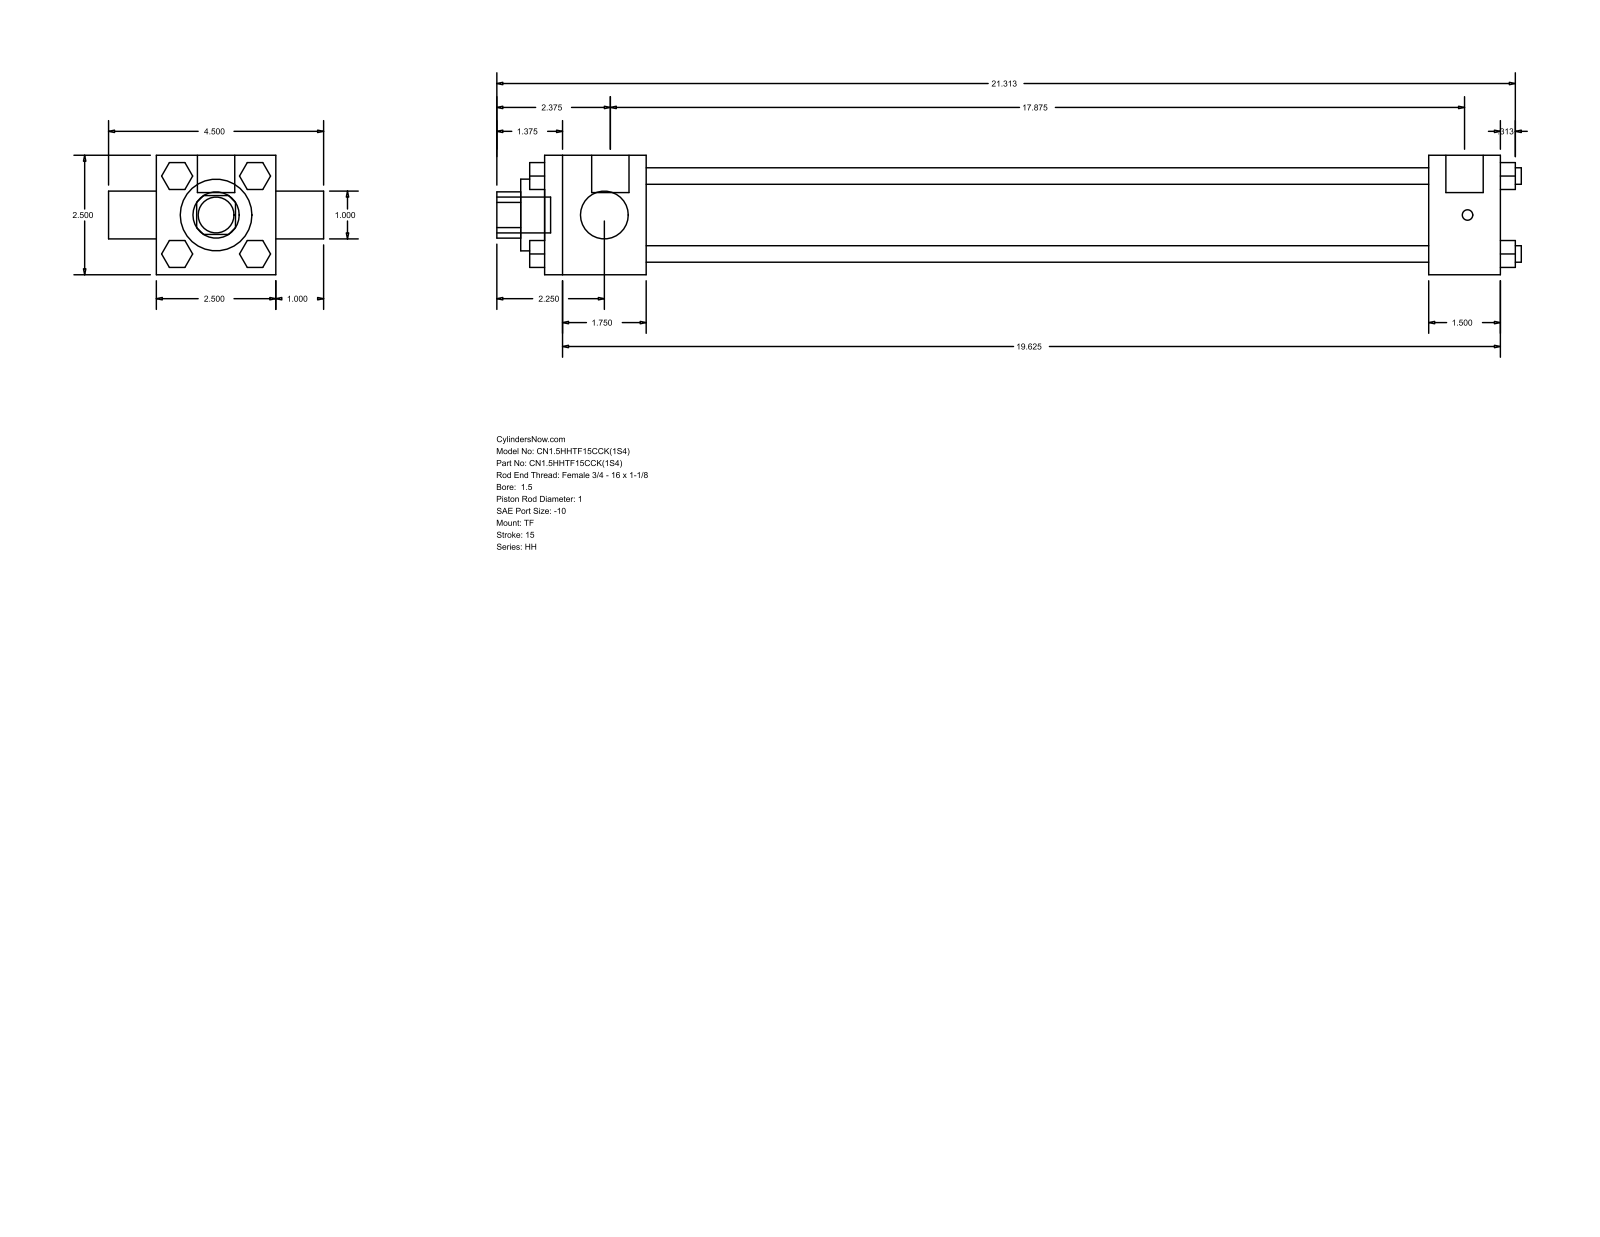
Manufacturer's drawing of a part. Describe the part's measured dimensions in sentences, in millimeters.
The part is named "HH_TF__0150_1". Its 3-D file was written by "GSSL Pune (CONFIG_CONTROL_DESIGN)". It is 0 solids with 120 faces: 92 planar, 28 cylindrical and 0 other. Overall it measures 544.51 by 114.3 by 63.5 millimeters. Round holes: 2 of diameter 25.4, 1 of diameter 38.1, 1 of diameter 44.45. Round bosses or shafts: 4 of diameter 8.76, 3 of diameter 5.56, 2 of diameter 19.84, 1 of diameter 19.05. Partial cylindrical surfaces (rounded edges, fillets, slot ends): 1 of radius 12.29. The main face-to-face distances are 63.5, 454.02, 415.92, 38.1, 53.98, 469.9, 508, 515.94, 25.4, 20.7.
